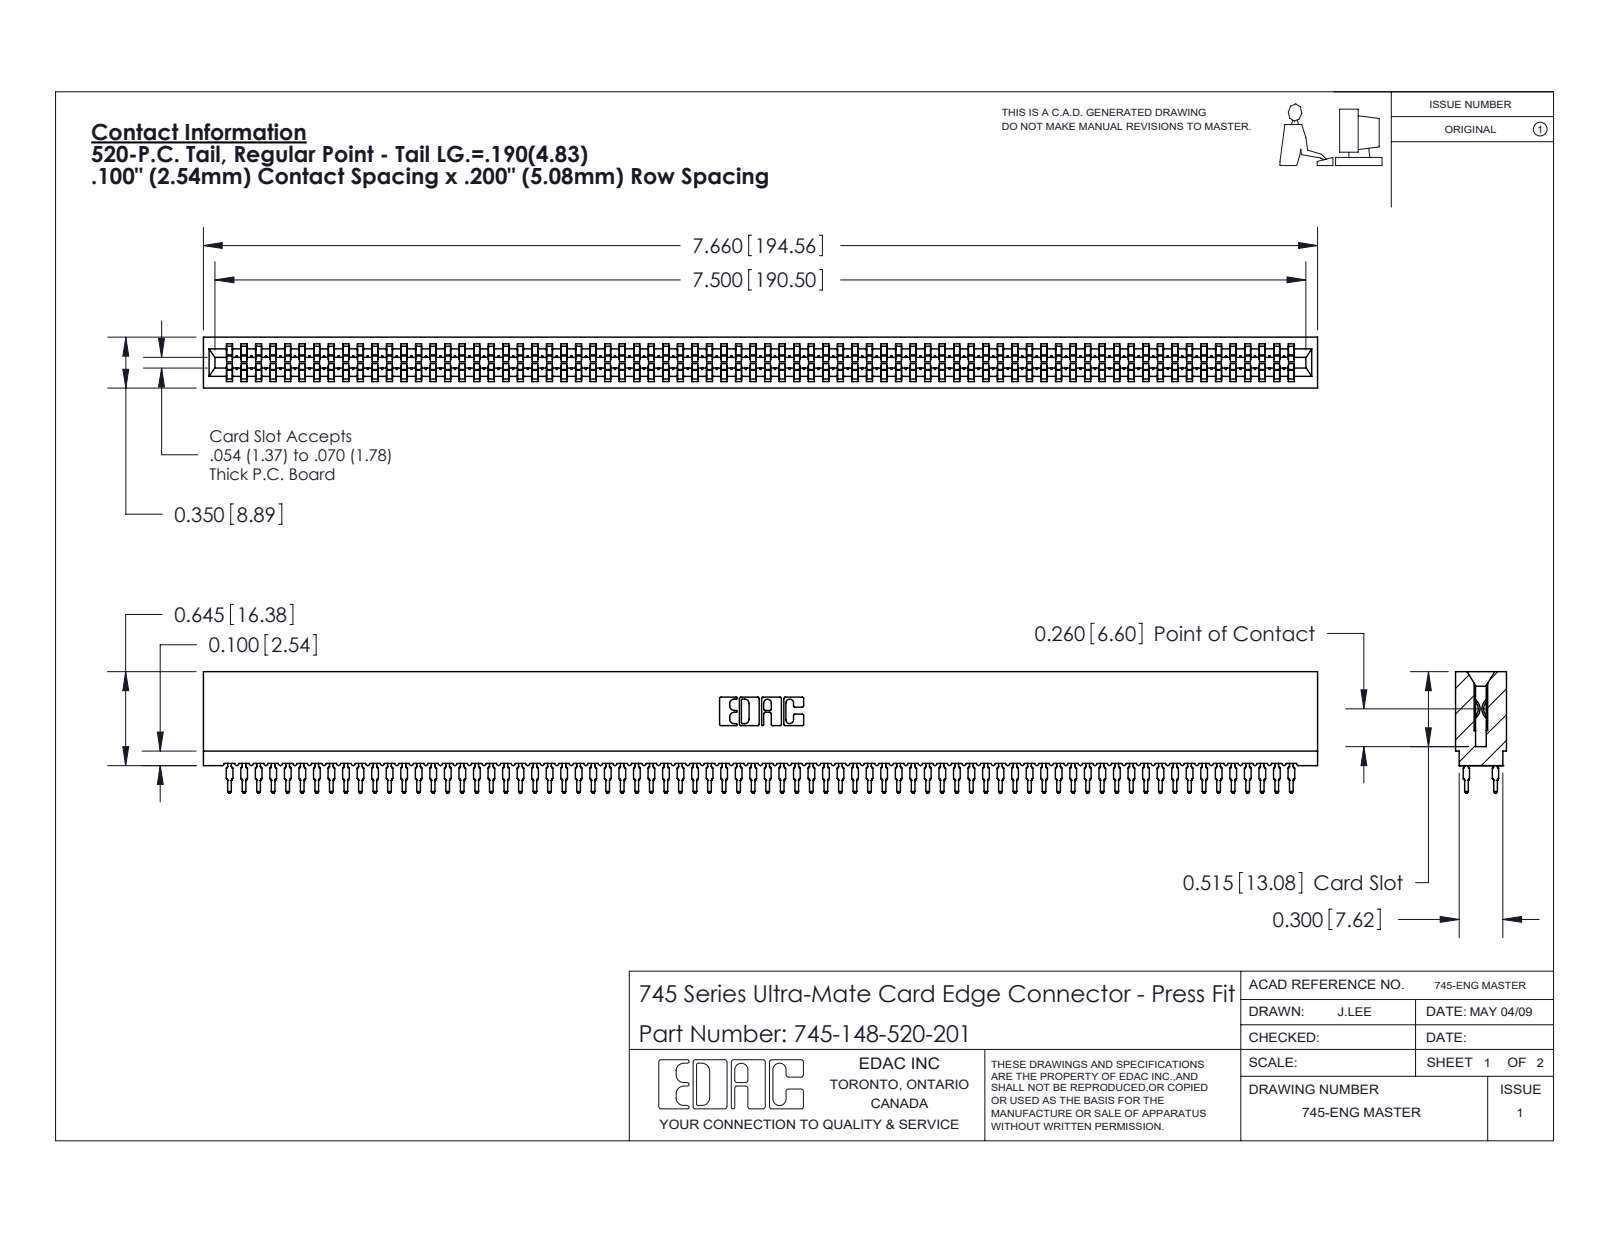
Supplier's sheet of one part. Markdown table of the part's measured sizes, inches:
| quantity | value |
| --- | --- |
| part name | 745 Part_Insulator Option - 01; 745-148-520-201; 745-292-001_520 |
| STEP written by | SolidWorks 2020 (CONFIG_CONTROL_DESIGN) |
| units | inches |
| bodies | 149 solids, 13341 faces (6863 planar, 2630 cylindrical, 3848 other) |
| overall size | 7.66 × 0.836 × 0.35 |
| volume | 1.05 in³ |
| surface area | 54.3 in² |
| partial cylindrical surfaces (radius × count) | 0.021 × 296, 0.015 × 148, 0.01 × 22, 0.005 × 8, 0.011 × 8, 0.007 × 6, 0.031 × 6, 0.026 × 3 |
| main face-to-face distances | 0.35, 0.063, 0.287, 0.045, 0.305, 0.018, 0.243, 0.138, 0.212, 0.093 |
